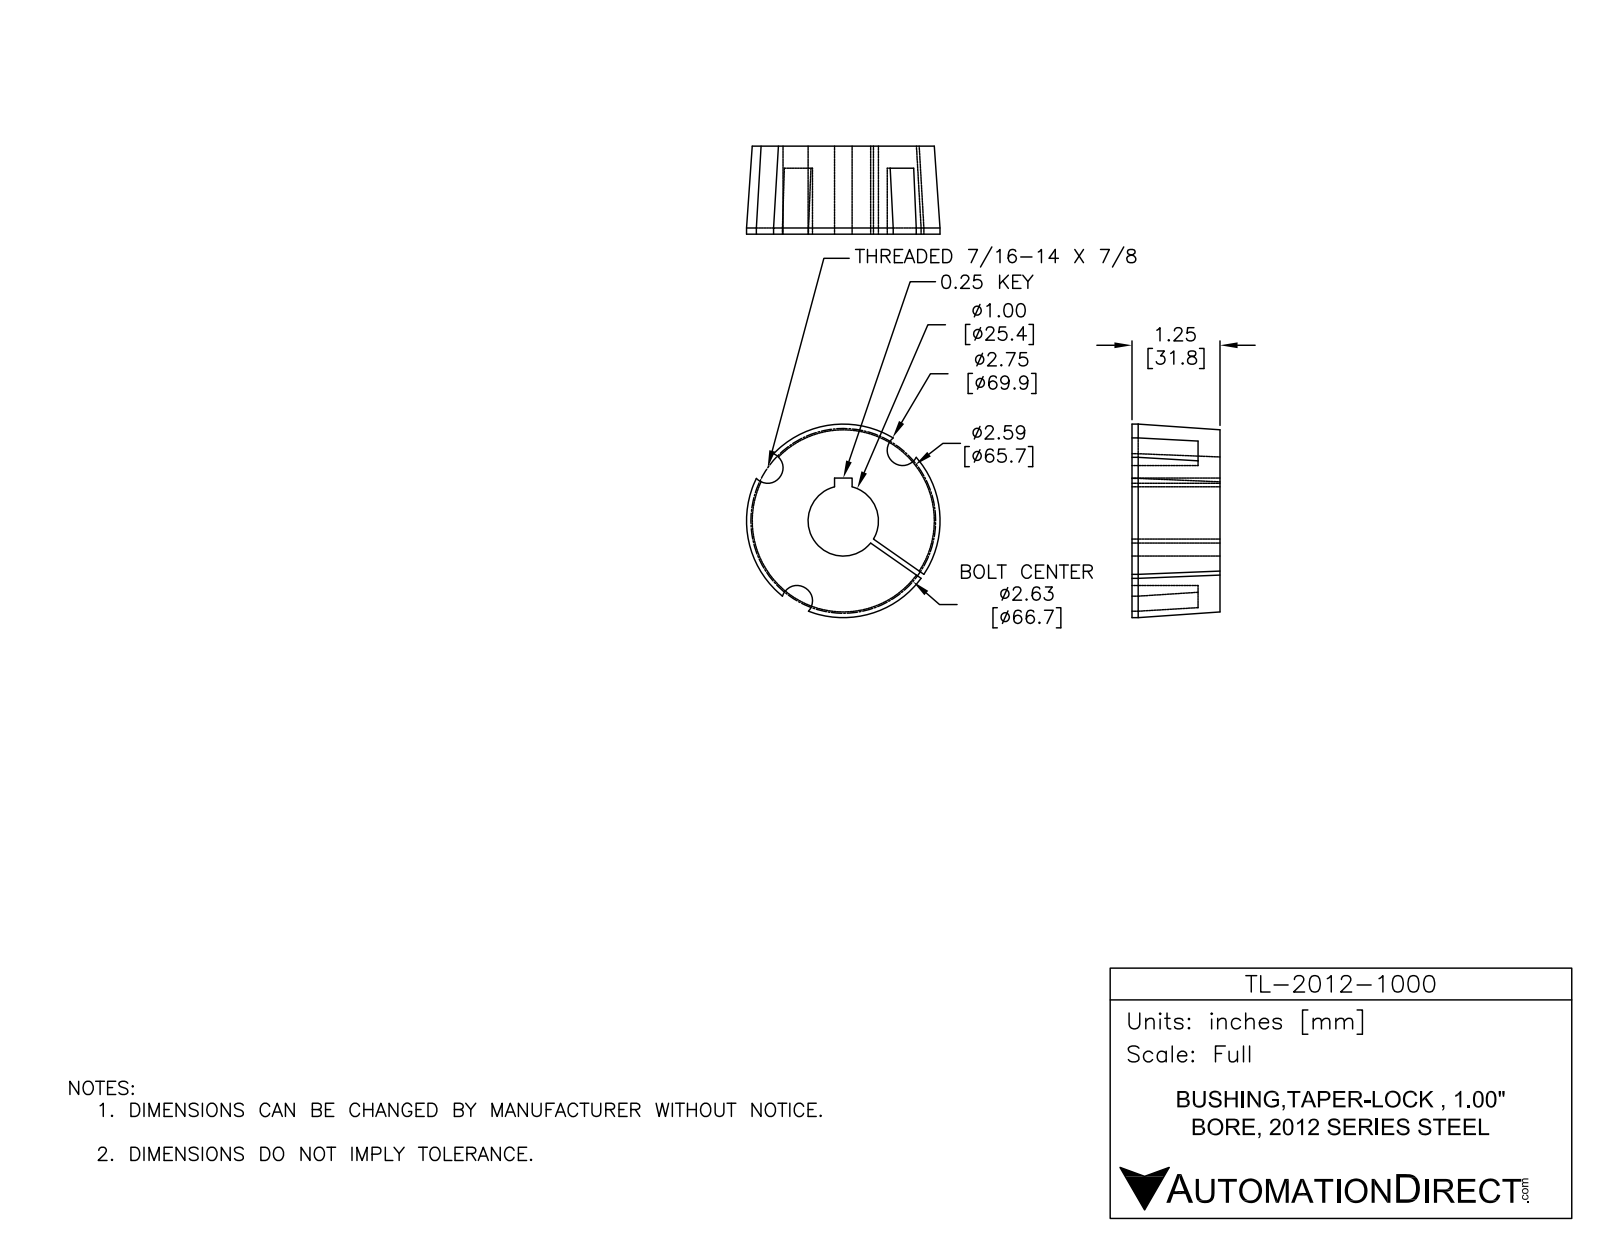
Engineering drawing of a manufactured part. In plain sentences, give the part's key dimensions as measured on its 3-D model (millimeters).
The part is named "TL-2012-1000". Its 3-D file was written by "SolidWorks 2014 (AUTOMOTIVE_DESIGN)". It is 1 solid with 24 faces: 9 planar, 12 cylindrical and 3 other. Overall it measures 69.9 by 69.9 by 31.8 millimeters. Its volume is 92 830 cubic millimeters and its surface area 17 280 square millimeters. Round holes: 1 of diameter 25.4. Round bosses or shafts: 1 of diameter 69.9. Partial cylindrical surfaces (rounded edges, fillets, slot ends): 3 of radius 5.6. The main face-to-face distances are 31.8, 1.8, 6.4, 8, 23.8.
